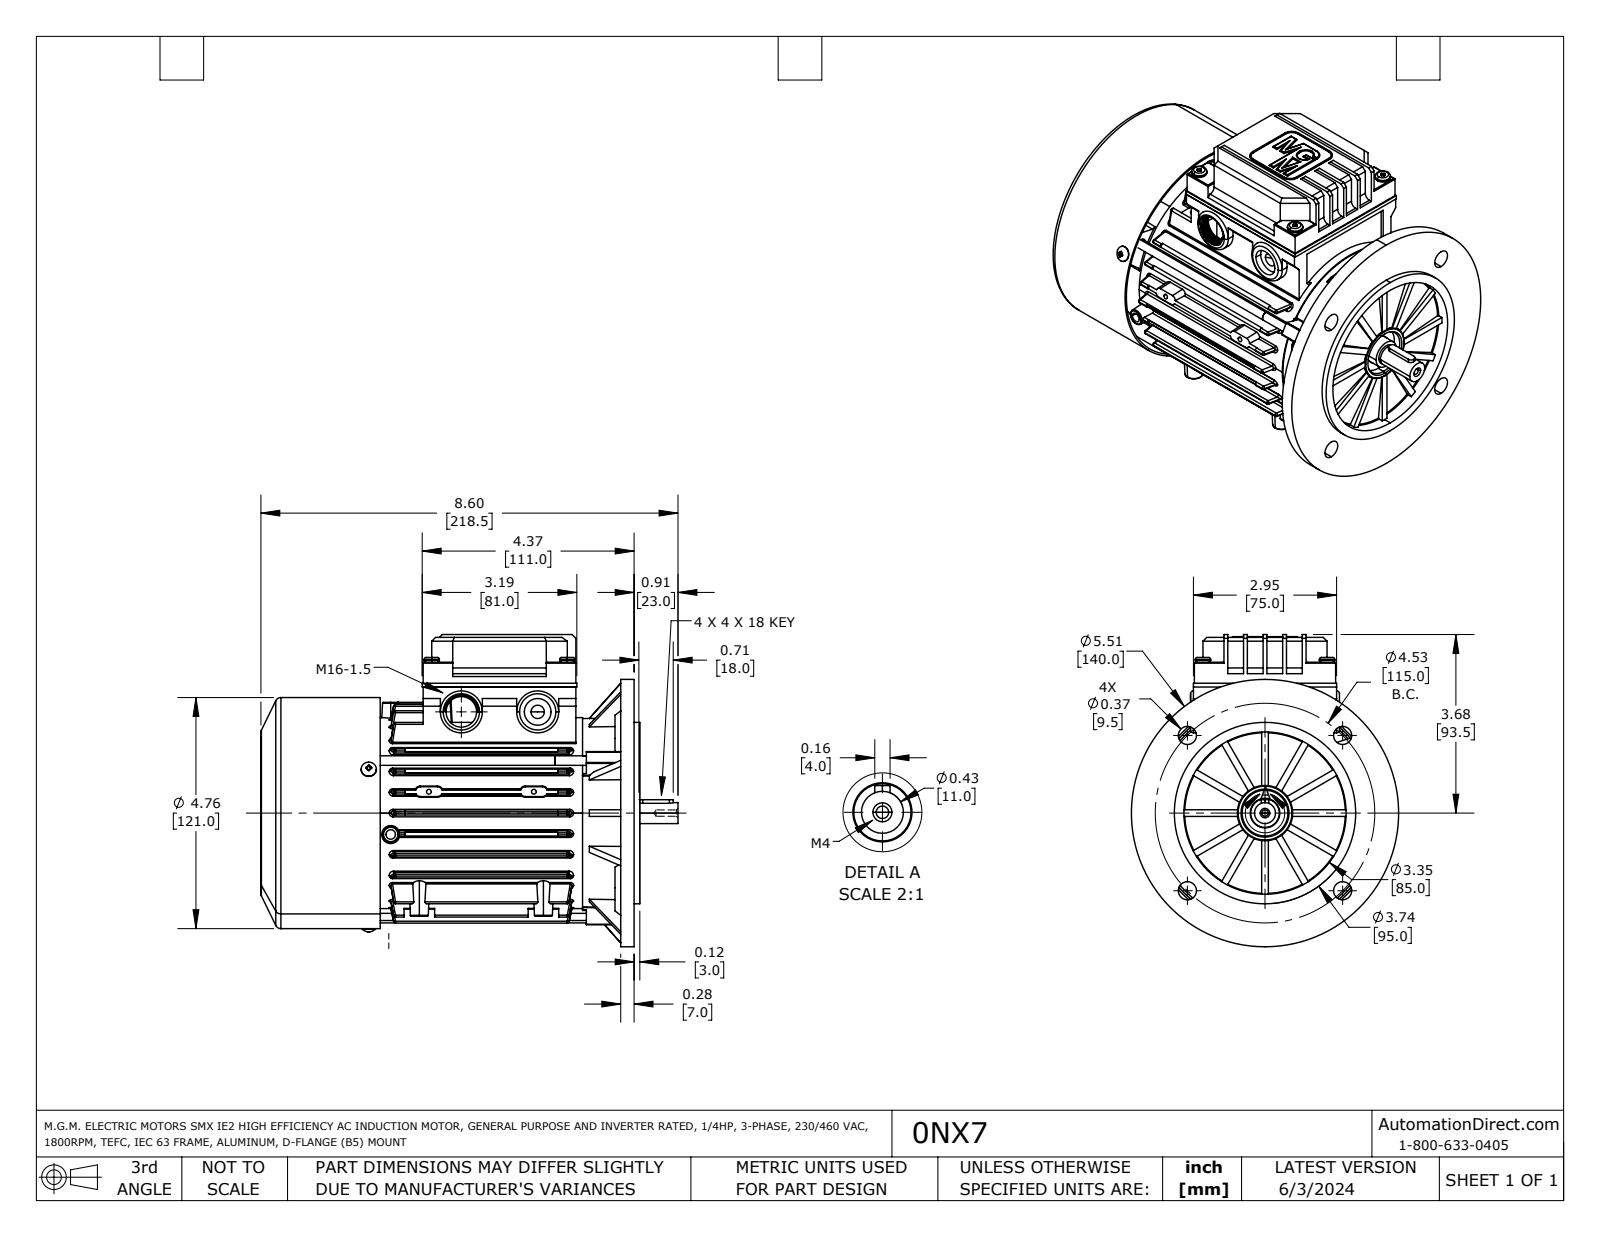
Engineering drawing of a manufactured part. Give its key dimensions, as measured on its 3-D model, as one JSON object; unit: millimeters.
{"part_name": "0NX7", "step_written_by": "SolidWorks 2021 (AUTOMOTIVE_DESIGN)", "units": "millimeters", "bodies": {"solids": 22, "faces": 3150, "planar": 1116, "cylindrical": 1031, "other": 1003}, "overall_size": [218.5, 163.5, 140], "volume_mm3": 521300, "surface_area_mm2": 330300, "round_holes": [[3, 12], [3.3, 8], [4, 7], [5.5, 7], [5, 6], [9.5, 4], [3.2, 3], [4.2, 3], [6, 3], [7, 3], [2.5, 2], [16, 2]], "round_bosses_or_shafts": [[3, 10], [8, 7], [3.5, 4], [5, 3], [2, 3], [140, 1], [121, 1], [100, 1]], "partial_cylinders_radius": [[1, 281], [0.4, 42], [0.5, 36], [0.2, 32], [0.1, 16], [0.8, 16], [0.4, 12], [0.9, 12]], "face_to_face_distances": [2, 11, 22, 24, 33, 13, 20, 3.5, 1.5, 100], "hole_center_spacings": [94.4, 11.5, 11.6, 13.7, 19.5, 28.5, 30.8, 31]}
